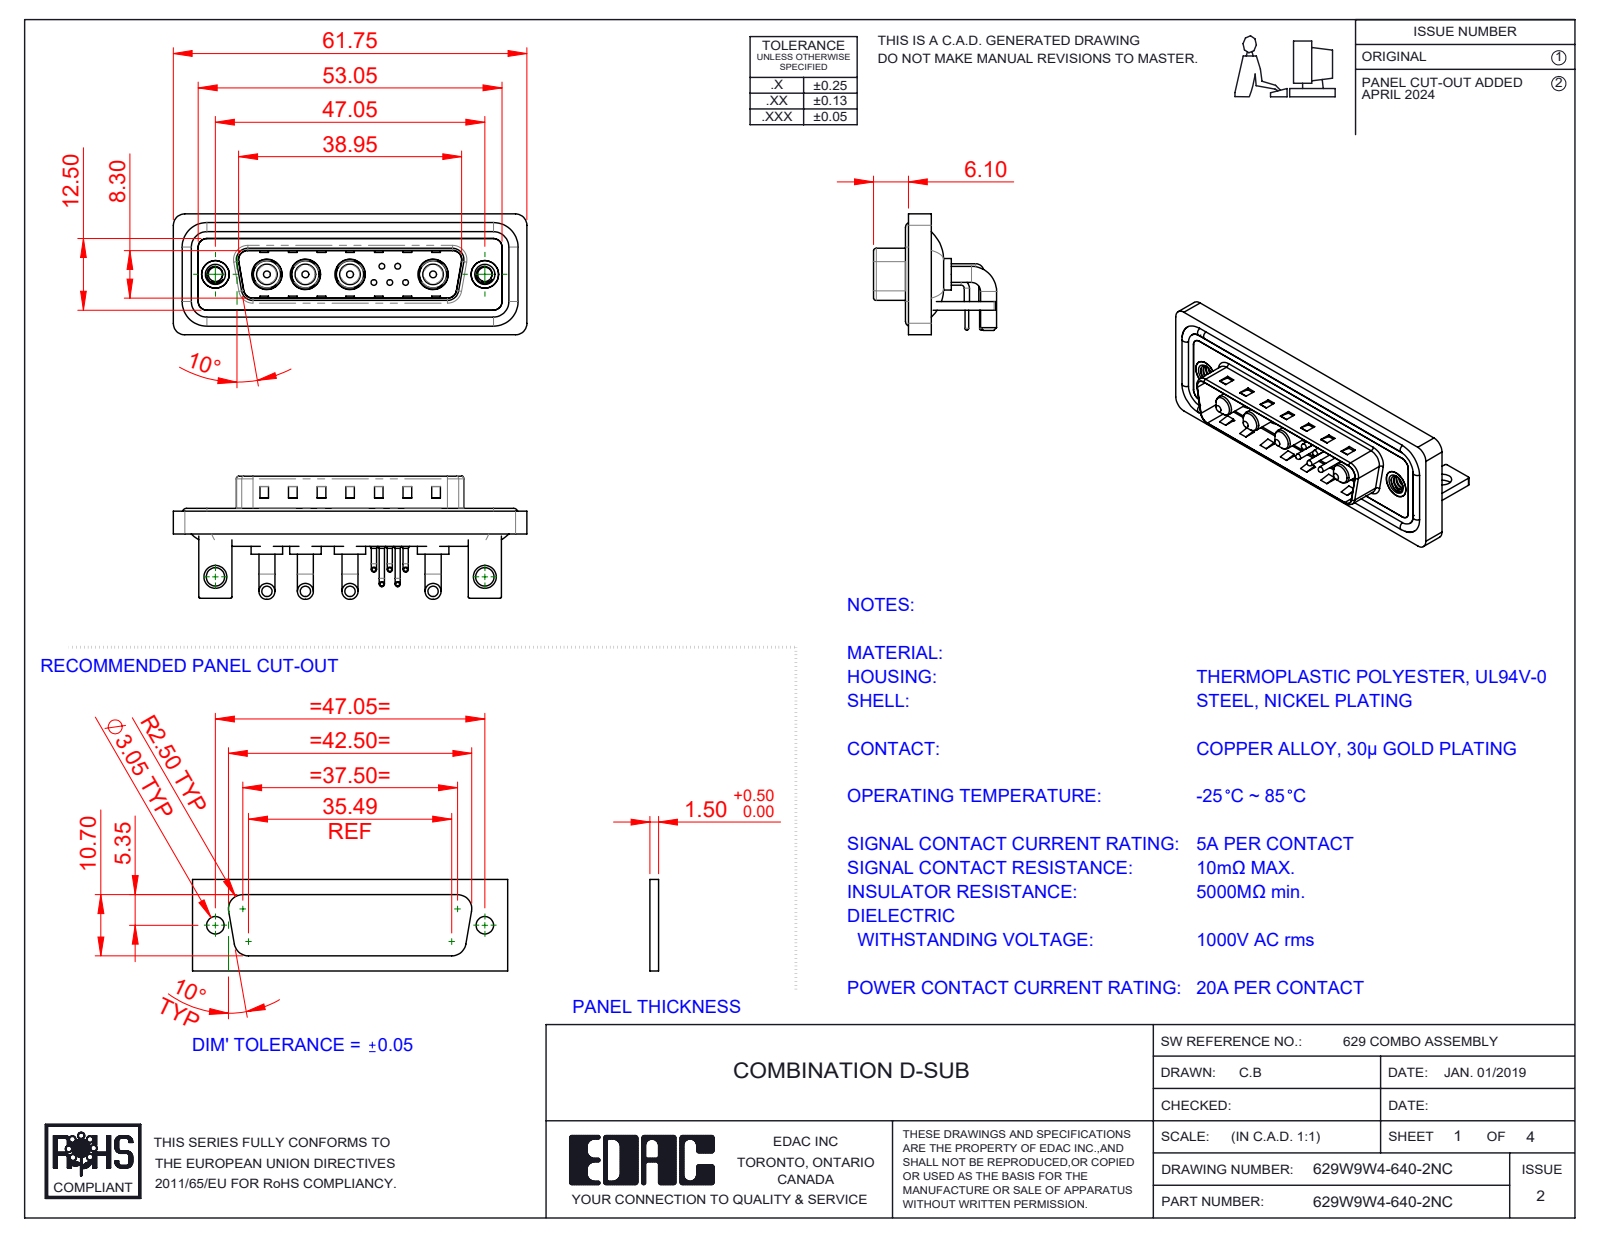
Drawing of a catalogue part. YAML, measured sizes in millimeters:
part_name: "Power Pin_20A RA; 629Combo Contact Row 1; 629Combo Contact Row 2; 629Combo Housing_9W4 (+6 more)"
step_written_by: "SolidWorks 2023 (CONFIG_CONTROL_DESIGN)"
units: millimeters
bodies: {solids: 22, faces: 1243, planar: 589, cylindrical: 470, other: 184}
overall_size: [61.75, 21.5, 21.1]
volume: 7976
surface_area: 12964
round_holes:
  - {diameter: 0.75, count: 5}
  - {diameter: 1.6, count: 5}
  - {diameter: 2, count: 5}
  - {diameter: 4.85, count: 4}
  - {diameter: 5.3, count: 4}
  - {diameter: 2.5, count: 2}
  - {diameter: 3.2, count: 2}
  - {diameter: 4, count: 2}
  - {diameter: 4.8, count: 2}
  - {diameter: 5, count: 2}
round_bosses_or_shafts:
  - {diameter: 0.9, count: 10}
  - {diameter: 2.8, count: 8}
  - {diameter: 1.5, count: 5}
  - {diameter: 1, count: 5}
  - {diameter: 0.65, count: 5}
  - {diameter: 5.5, count: 4}
  - {diameter: 5.2, count: 4}
  - {diameter: 4.75, count: 4}
partial_cylinders:
  - {radius: 2, count: 19}
  - {radius: 1.5, count: 18}
  - {radius: 0.25, count: 16}
  - {radius: 0.5, count: 9}
  - {radius: 1.6, count: 8}
  - {radius: 1.01, count: 5}
  - {radius: 0.6, count: 4}
  - {radius: 0.65, count: 4}
face_to_face_distances: [0.4, 1.5, 0.8, 2.9, 2.1, 1.1, 3.7, 4.1, 4.5, 1.6]
hole_center_spacings: [3.16, 2.77, 5.04, 14.5, 47.05, 2.78, 4.4, 4.41]
